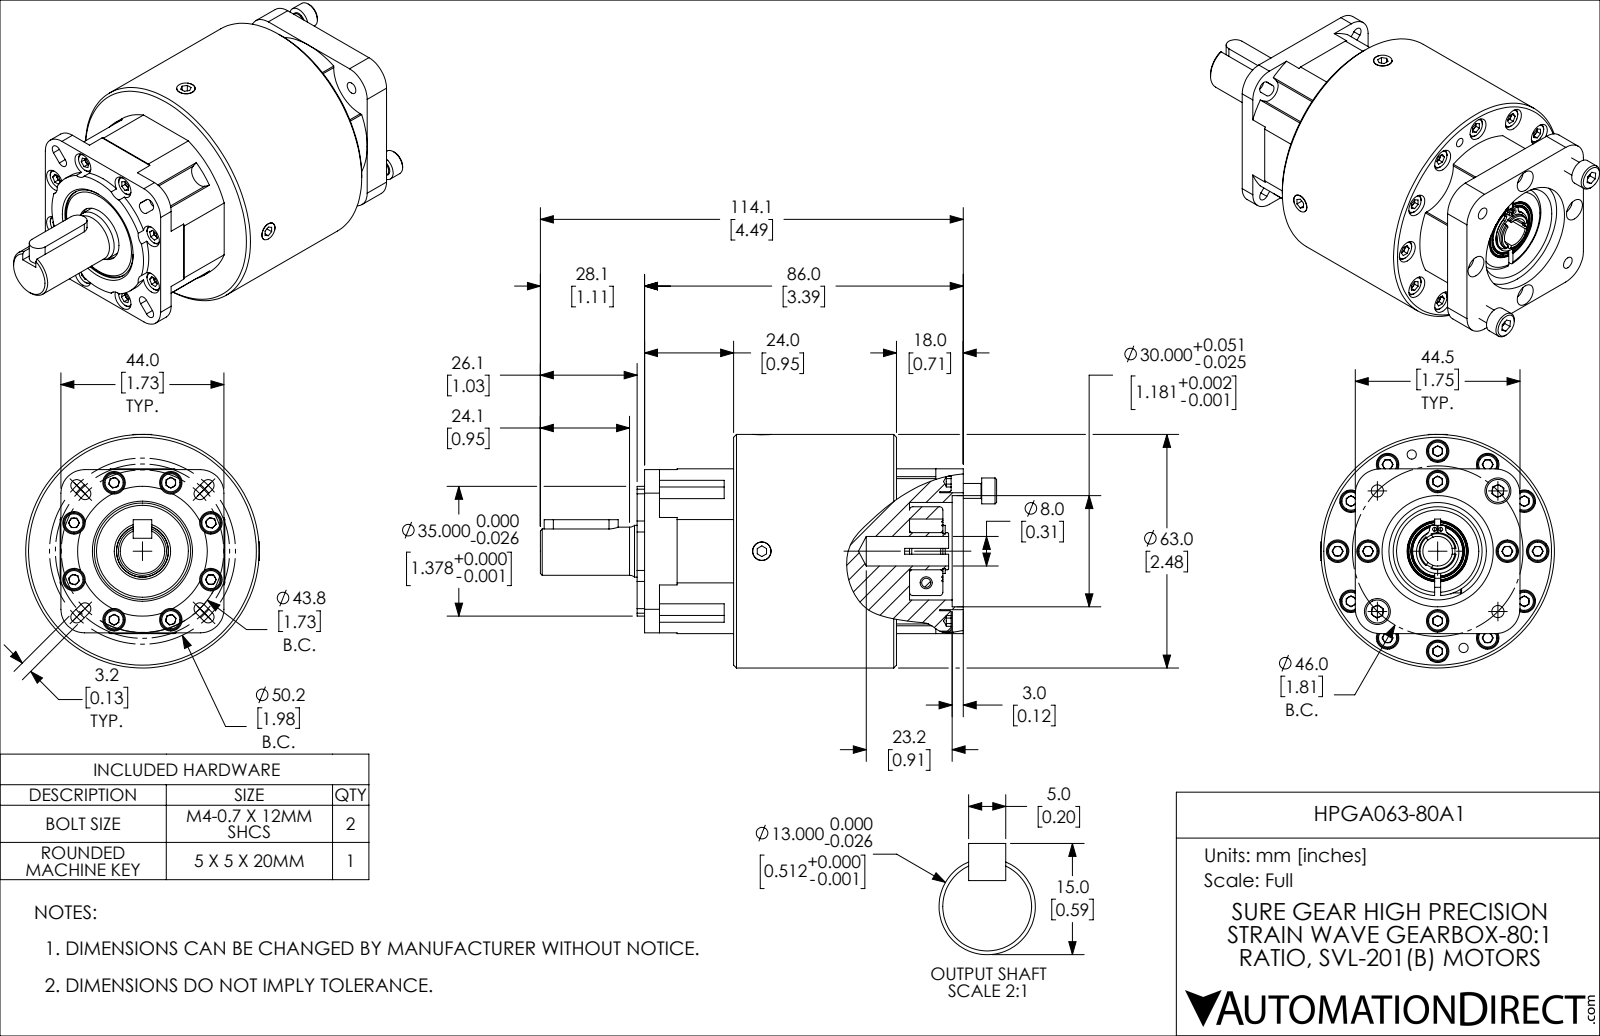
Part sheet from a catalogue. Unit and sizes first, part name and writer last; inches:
Units: inches
Overall size (bounding box): 4.847 × 2.48 × 2.48
Round holes (diameter × count): ⌀0.239 ×24, ⌀0.13 ×4, ⌀0.041 ×2, ⌀0.098 ×2, ⌀0.197 ×2, ⌀0.101 ×1, ⌀0.129 ×1, ⌀0.201 ×1, ⌀0.234 ×1, ⌀0.315 ×1, ⌀0.598 ×1, ⌀1.024 ×1
Round bosses / shafts (diameter × count): ⌀0.217 ×25, ⌀0.276 ×2, ⌀0.196 ×2, ⌀0.157 ×2, ⌀2.48 ×1, ⌀0.945 ×1, ⌀0.551 ×1, ⌀0.512 ×1
Partial cylindrical surfaces — rounded edges, fillets, slot ends (radius × count): R0.063 ×8, R0.125 ×4, R0.25 ×4, R0.265 ×4, R0.4 ×4, R0.5 ×3, R0.02 ×2, R0.059 ×2
Main face-to-face distances: 1.731, 2.439, 0.709, 1.741, 1.75, 0.946, 2.677, 3.386, 1.741, 3.095
Hole centre spacings: 1.063, 1.503, 1.841, 2.054, 0.3, 0.65, 1.664, 1.754
Volume: 12.42 in³ · Surface area: 52.39 in²
Bodies: 8 solids, 1004 faces (537 planar, 291 cylindrical, 176 other)
Part name (STEP PRODUCT): HPGA063-80A1
STEP written by: SolidWorks 2021 (CONFIG_CONTROL_DESIGN)
